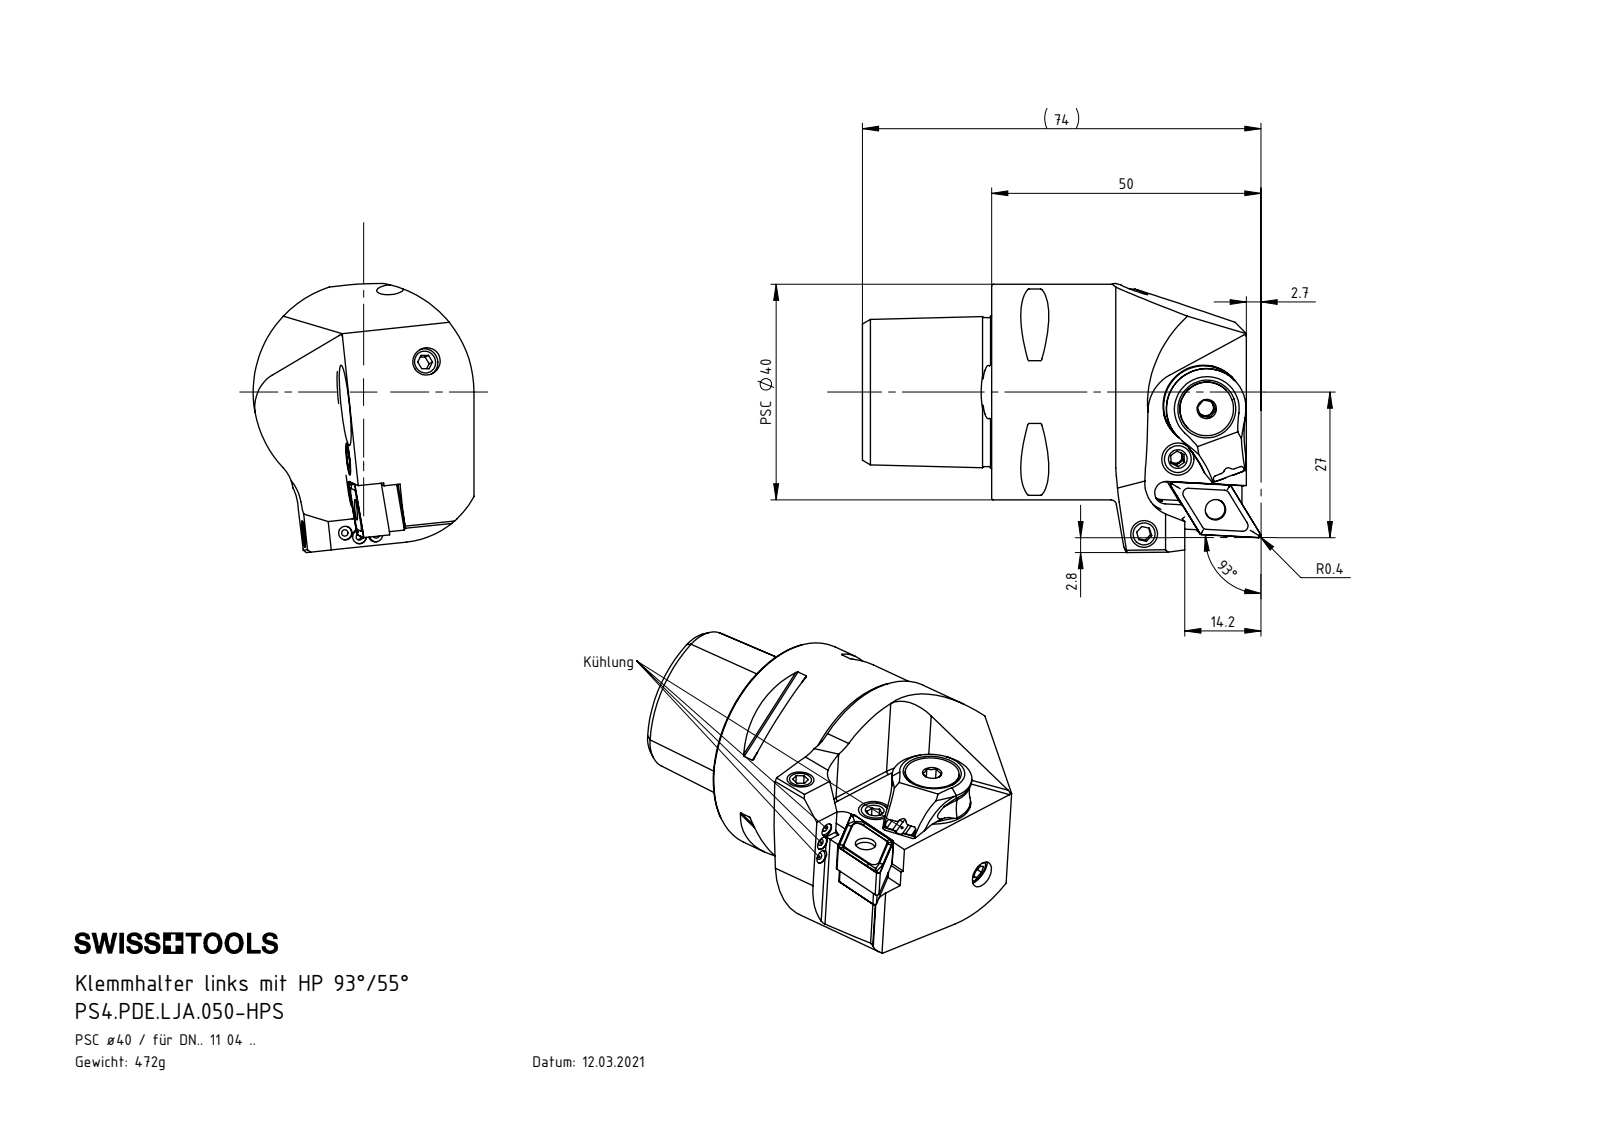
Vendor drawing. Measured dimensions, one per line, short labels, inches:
name: ISO 4026 - M5 x 5; DNMG110404; WDE-ER4.101.017_A; WDE-ER3.101.000_A (+8 more)
written by: SolidWorks 2017 (CONFIG_CONTROL_DESIGN)
unit: in
bodies: 14 solids, 619 faces (177 planar, 168 cylindrical, 274 other)
size: 2.913 × 1.966 × 1.614
volume: 3.721 in³; area: 30.24 in²
holes: 5× ⌀0.165, 4× ⌀0.047, 4× ⌀0.098, 3× ⌀0.197, 1× ⌀0.079, 1× ⌀0.15, 1× ⌀0.157, 1× ⌀0.181, 1× ⌀0.189, 1× ⌀0.209, 1× ⌀0.252, 1× ⌀0.492
bosses: 4× ⌀0.197, 1× ⌀1.575, 1× ⌀0.585, 1× ⌀0.528, 1× ⌀0.394, 1× ⌀0.236, 1× ⌀0.232, 1× ⌀0.113
rounds: 9× R0.012, 8× R0.016, 7× R0.02, 7× R0.039, 5× R0.276, 4× R0.083, 3× R0.236, 2× R0.043
face distances: 0.354, 0.787, 0.945, 0.177, 0.182, 0.021, 0.118, 0.611, 0.059, 0.125
hole spacings: 0.451, 0.677, 1.021, 0.177, 0.178, 0.435, 0.465, 0.577
